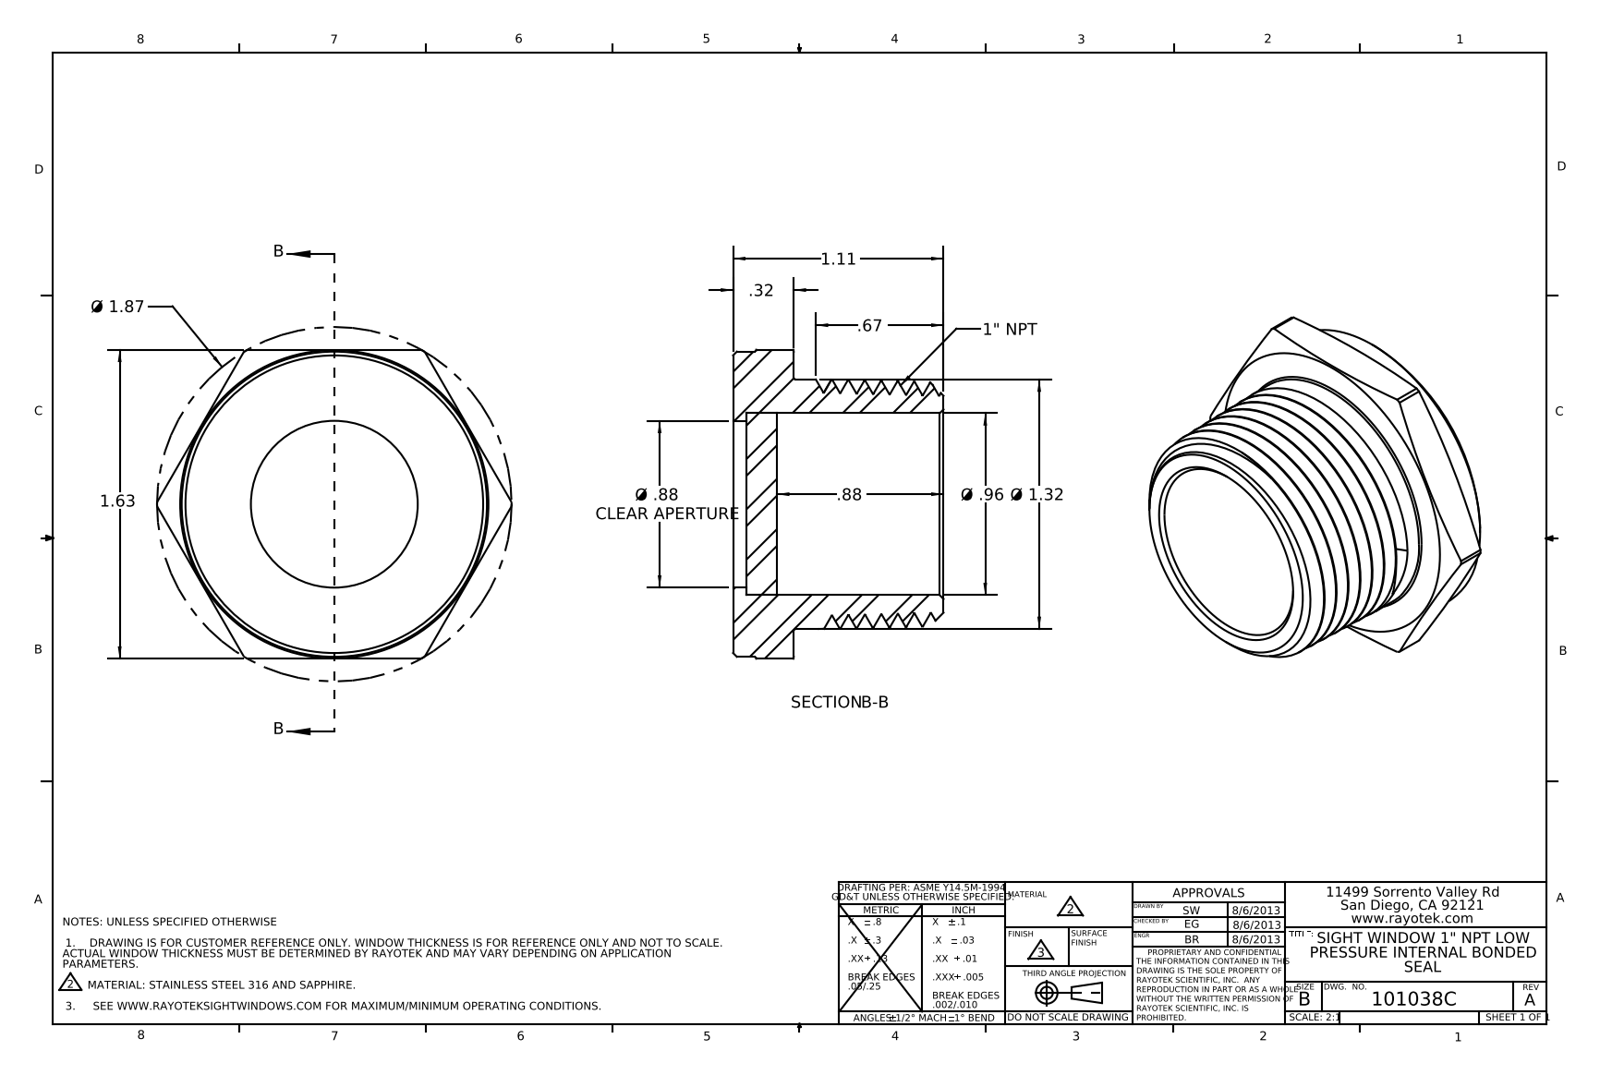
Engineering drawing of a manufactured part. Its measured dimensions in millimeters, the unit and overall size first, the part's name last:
Units: millimetres
Overall size (bounding box): 47.5 × 41.4 × 28.2
Round holes (diameter × count): ⌀22.4 ×1, ⌀24.4 ×1
Round bosses / shafts (diameter × count): ⌀40.9 ×1, ⌀33.4 ×1
Partial cylindrical surfaces — rounded edges, fillets, slot ends (radius × count): R23.7 ×1
Main face-to-face distances: 1.8, 5.9, 4.1, 8.1, 6.3, 2.2, 41.4, 28.2, 26.4, 22.3
Volume: 16 100 mm³ · Surface area: 9 761 mm²
Bodies: 2 solids, 65 faces (15 planar, 17 cylindrical, 33 other)
Part name (STEP PRODUCT): 403038
STEP written by: SolidWorks 2012 (AUTOMOTIVE_DESIGN)
